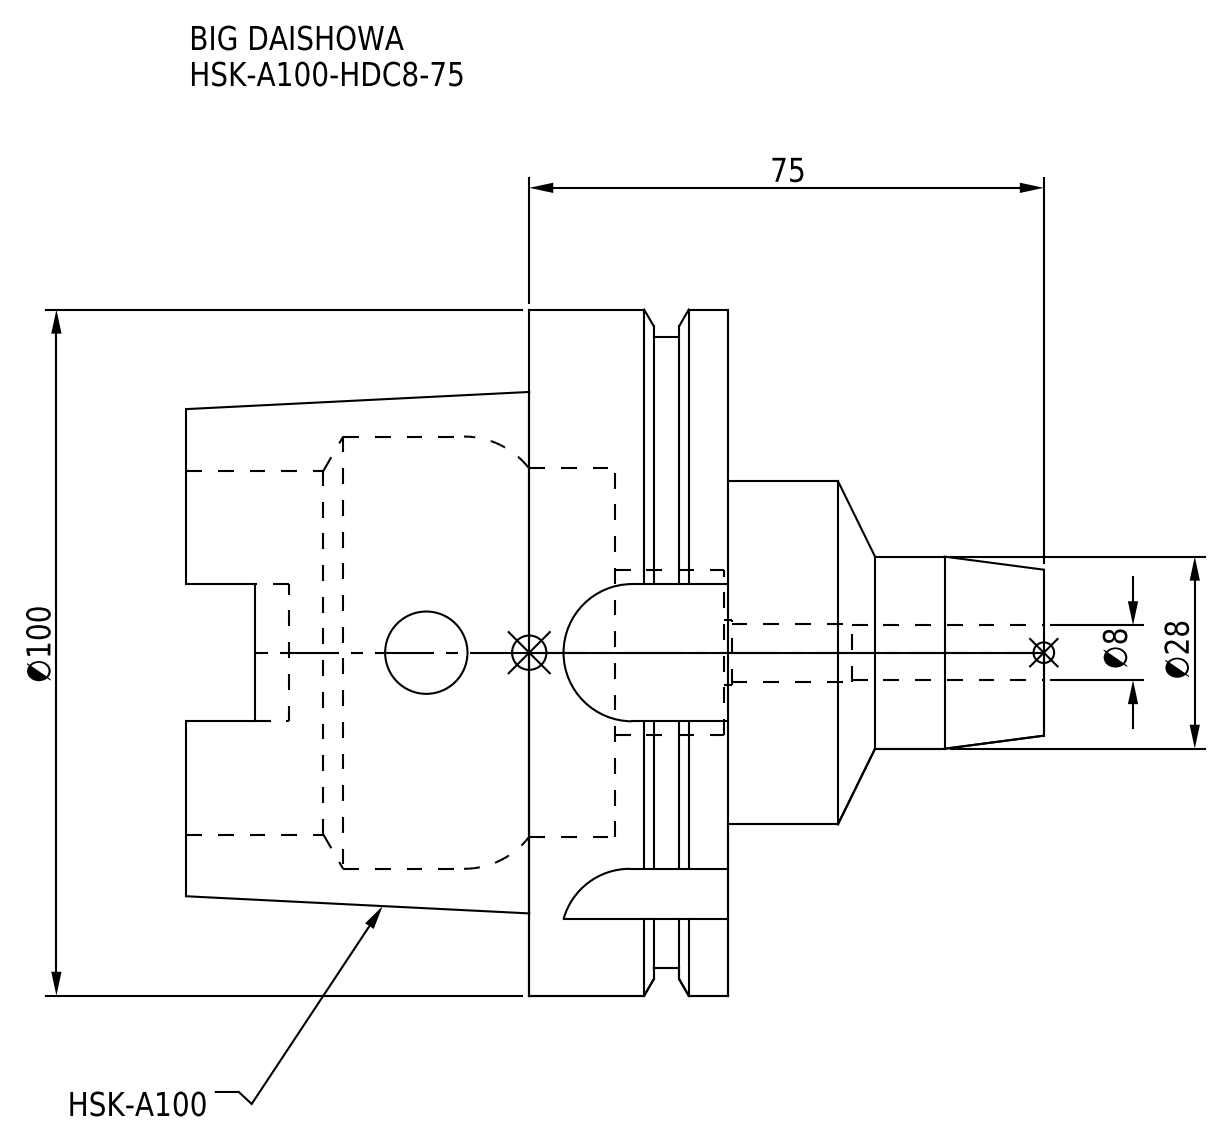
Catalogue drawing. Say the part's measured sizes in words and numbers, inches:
The part is named "HSK-A100-HDC8-75". Its 3-D file was written by "CREO PARAMETRIC BY PTC INC, 2016380 (AUTOMOTIVE_DESIGN)". It is 1 solid with 92 faces: 34 planar, 40 cylindrical and 18 other. Overall it measures 4.921 by 3.937 by 3.937 inches. Its volume is 18.49 cubic inches and its surface area 86.33 square inches. Round holes: 1 of diameter 0.315, 1 of diameter 0.335, 1 of diameter 0.374, 1 of diameter 0.472, 1 of diameter 0.945, 1 of diameter 2.087, 1 of diameter 2.118, 1 of diameter 2.48. Round bosses or shafts: 1 of diameter 3.937, 1 of diameter 3.622, 1 of diameter 1.969, 1 of diameter 1.102. Partial cylindrical surfaces (rounded edges, fillets, slot ends): 4 of radius 0.192, 4 of radius 0.394. The main face-to-face distances are 1.142, 0.652, 0.49, 3.11, 2.459, 1.969, 2.091, 2.239, 3.465, 1.811.
